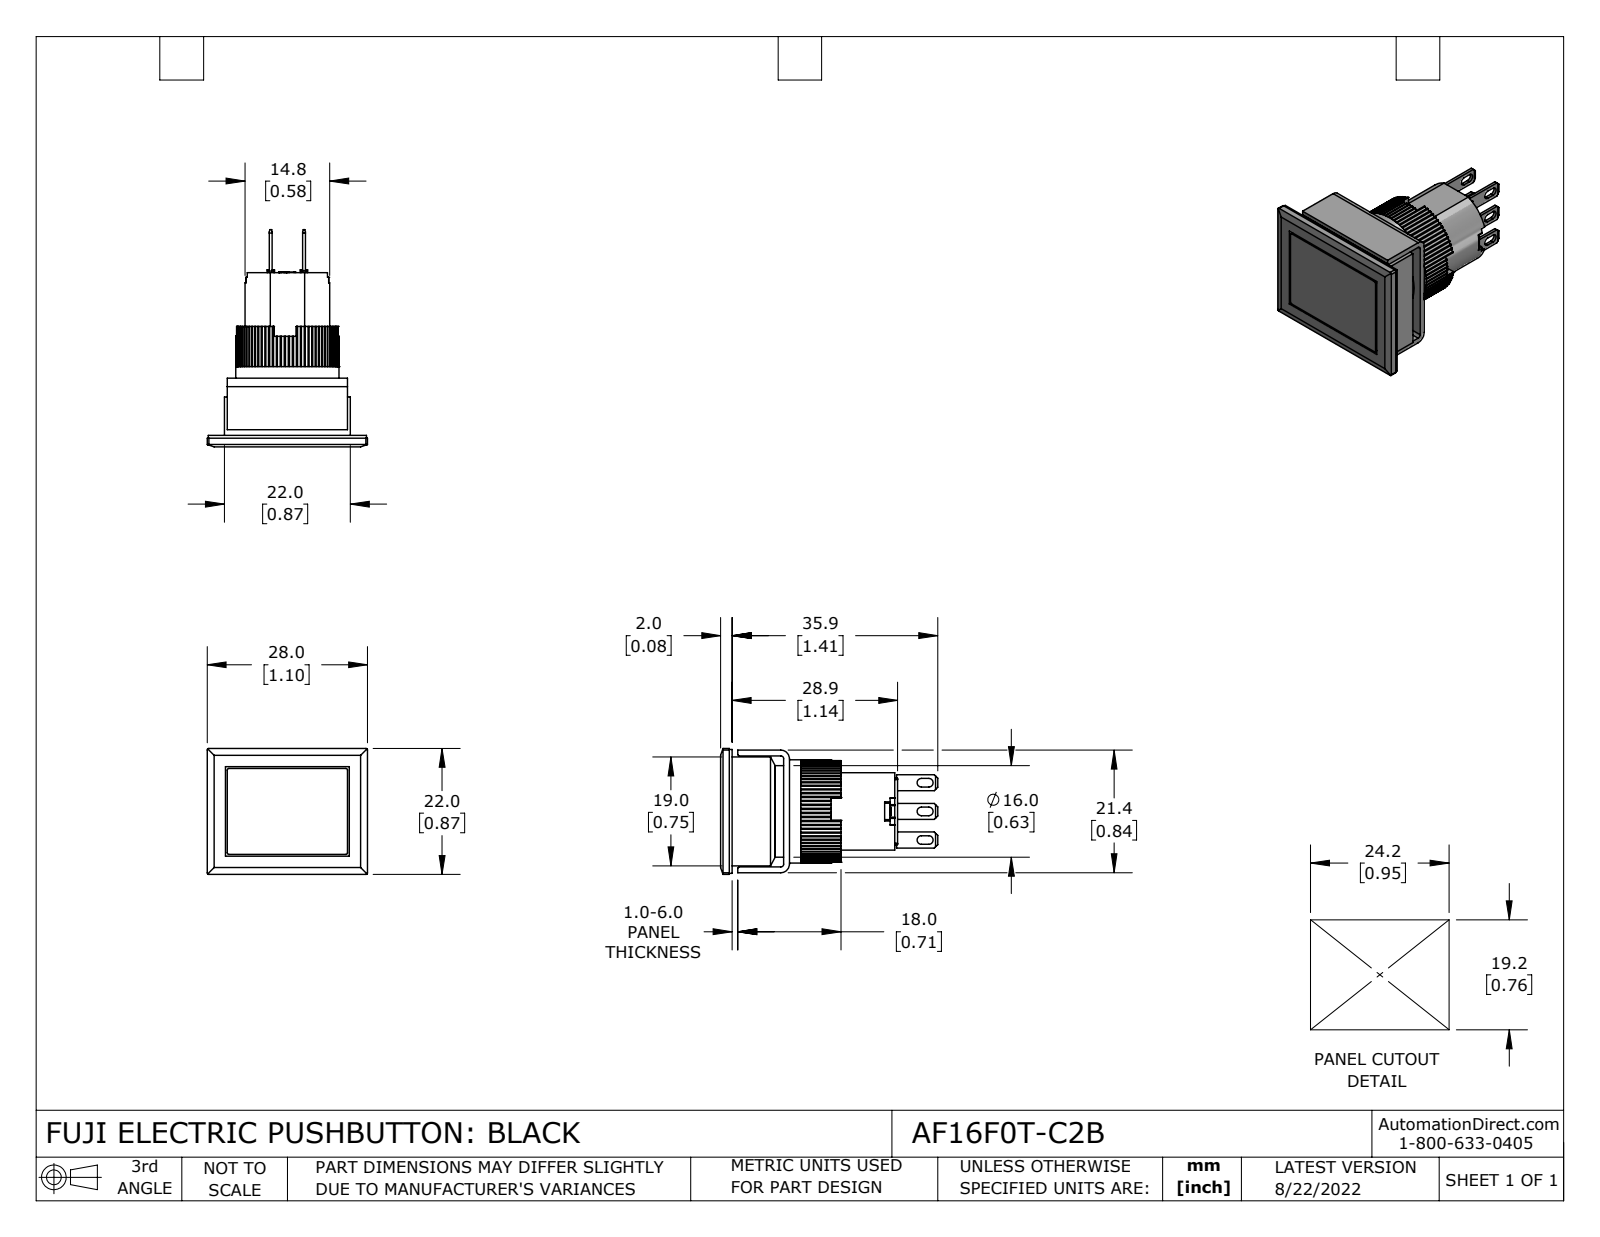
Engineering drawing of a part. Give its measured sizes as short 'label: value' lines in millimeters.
name: AF16F0T-C2B
written by: SolidWorks 2021 (CONFIG_CONTROL_DESIGN)
unit: mm
bodies: 12 solids, 798 faces (620 planar, 176 cylindrical, 2 other)
size: 37.9 × 28 × 22
volume: 8 870 mm³; area: 7 645 mm²
holes: 1× ⌀1, 1× ⌀18
bosses: 1× ⌀16, 1× ⌀14.8
rounds: 80× R0.3, 12× R0.2, 8× R0.3, 6× R0.8, 2× R0.5, 2× R1.5
face distances: 9.5, 1.5, 0.5, 3.6, 1, 8, 5.9, 2.1, 2, 19.2
